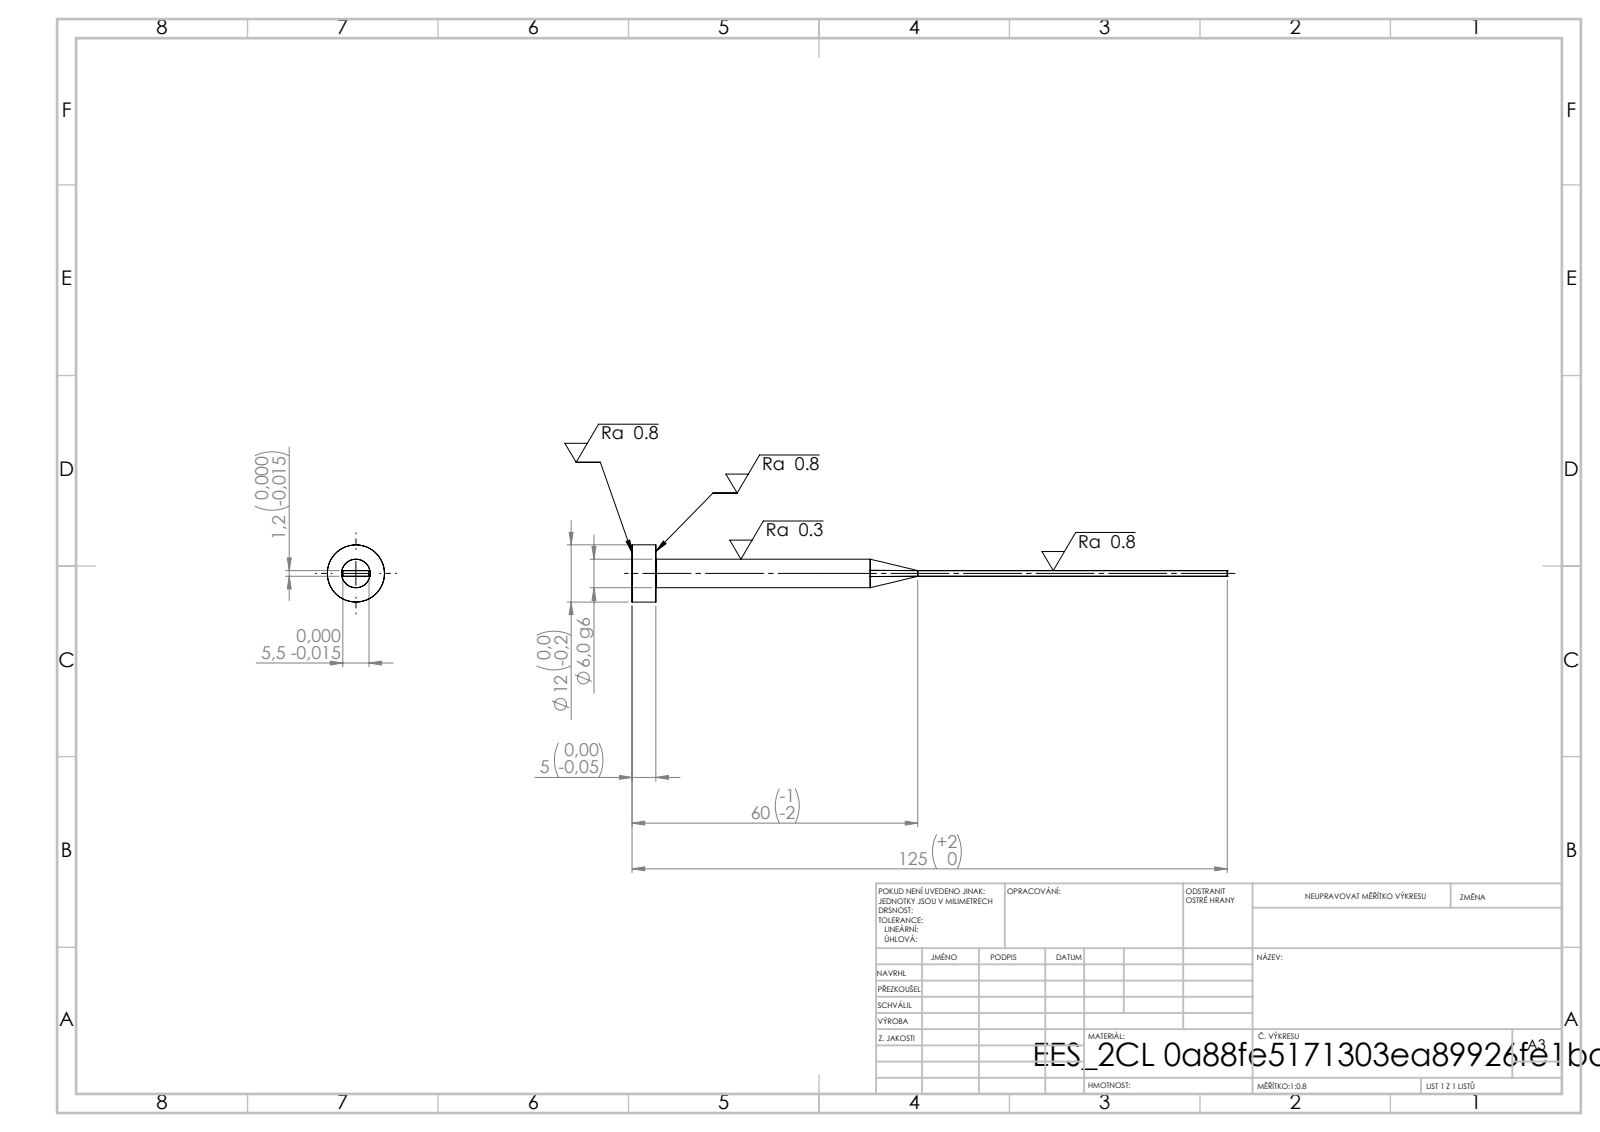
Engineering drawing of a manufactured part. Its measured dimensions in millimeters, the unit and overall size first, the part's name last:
Units: millimetres
Overall size (bounding box): 125 × 12 × 12
Round bosses / shafts (diameter × count): ⌀12 ×1, ⌀6 ×1
Main face-to-face distances: 1.2, 5, 5.5, 125, 120
Volume: 2 433 mm³ · Surface area: 2 269 mm²
Bodies: 1 solid, 15 faces (7 planar, 4 cylindrical, 4 other)
STEP written by: SolidWorks 2019 (CONFIG_CONTROL_DESIGN)
